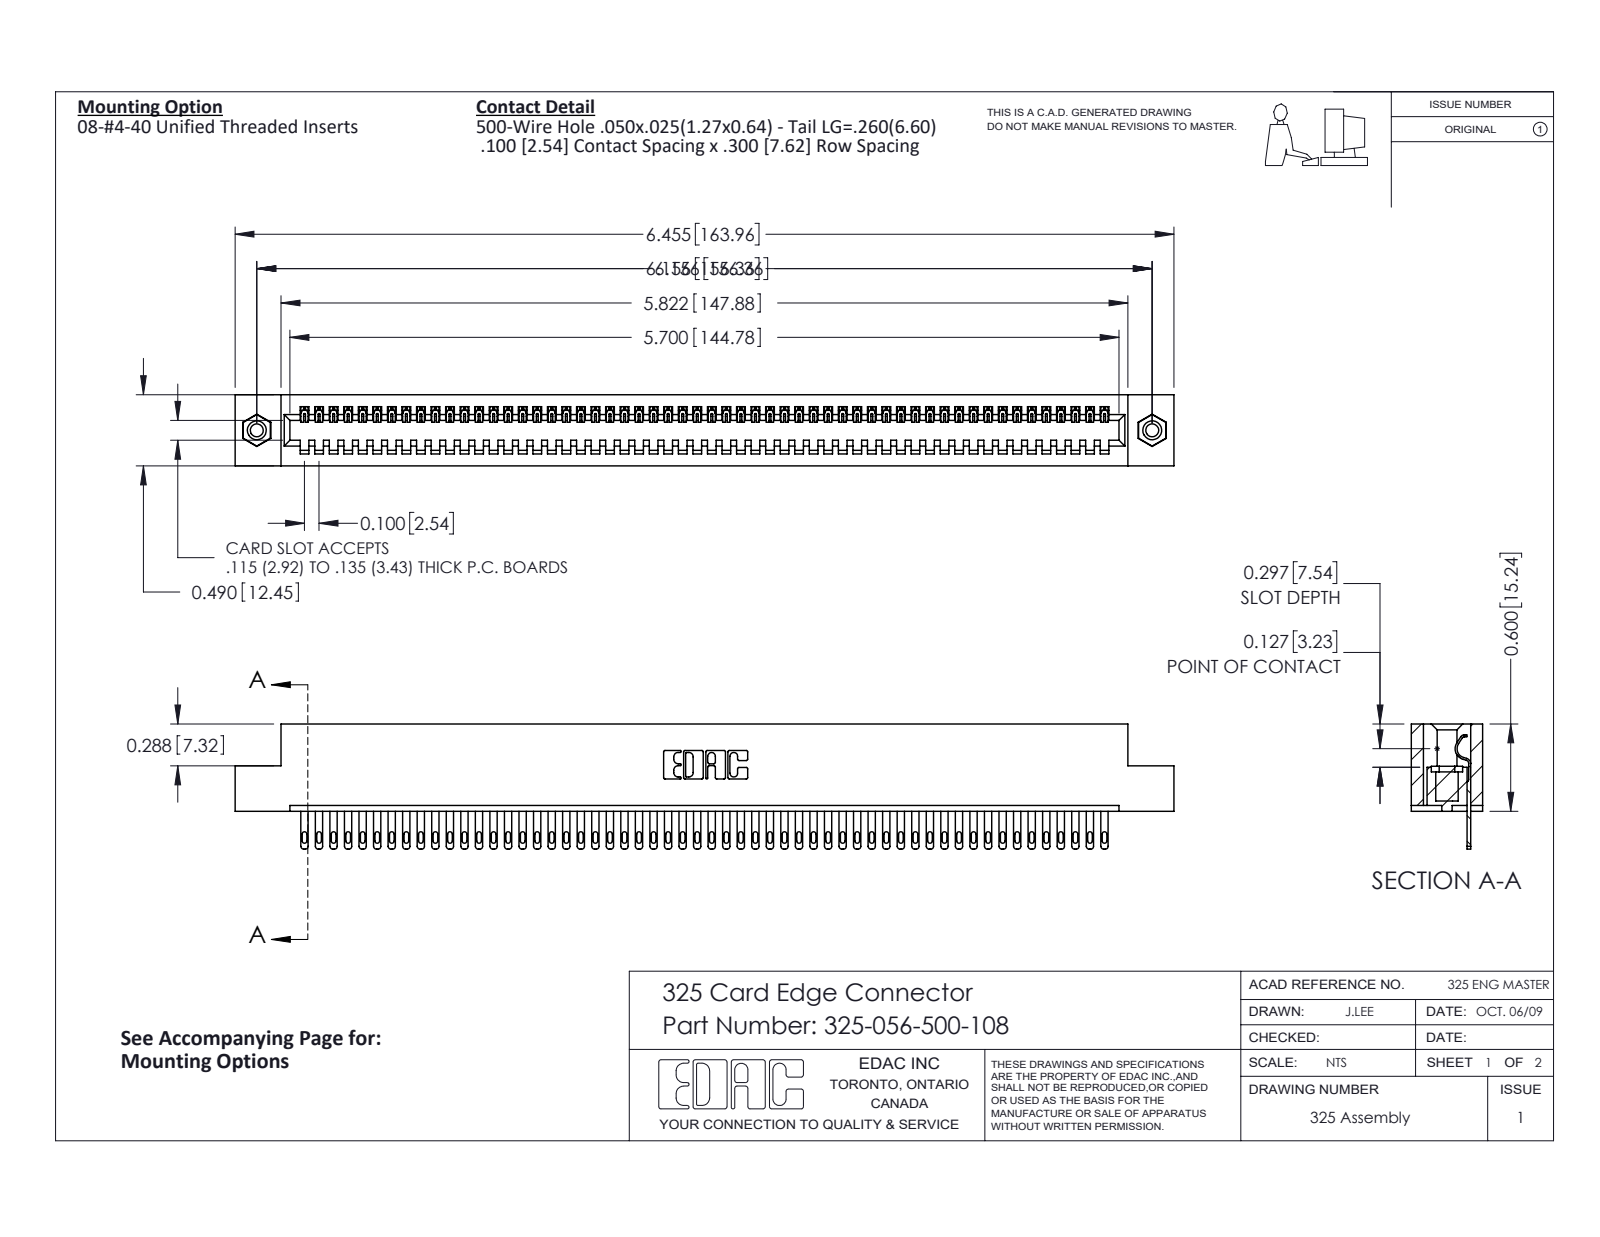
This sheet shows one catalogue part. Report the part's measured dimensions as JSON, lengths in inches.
{"part_name": "325-292-001_325-293-100; 345-250-001_345-250-003-102; 325-056-500-108; 325 Part_TI", "step_written_by": "SolidWorks 2016 (CONFIG_CONTROL_DESIGN)", "units": "inches", "bodies": {"solids": 59, "faces": 3198, "planar": 2118, "cylindrical": 1064, "other": 16}, "overall_size": [6.455, 0.86, 0.49], "volume_in3": 1.279, "surface_area_in2": 36.08, "round_holes": [[0.089, 2], [0.125, 2], [0.16, 2]], "round_bosses_or_shafts": [[0.155, 2]], "partial_cylinders_radius": [[0.006, 112], [0.016, 112], [0.02, 112], [0.01, 22], [0.007, 6], [0.031, 6], [0.026, 3], [0.014, 1]], "face_to_face_distances": [0.083, 0.407, 0.49, 0.107, 0.383, 0.025, 0.3, 0.325, 0.263, 0.56], "hole_center_spacings": [6.156]}
